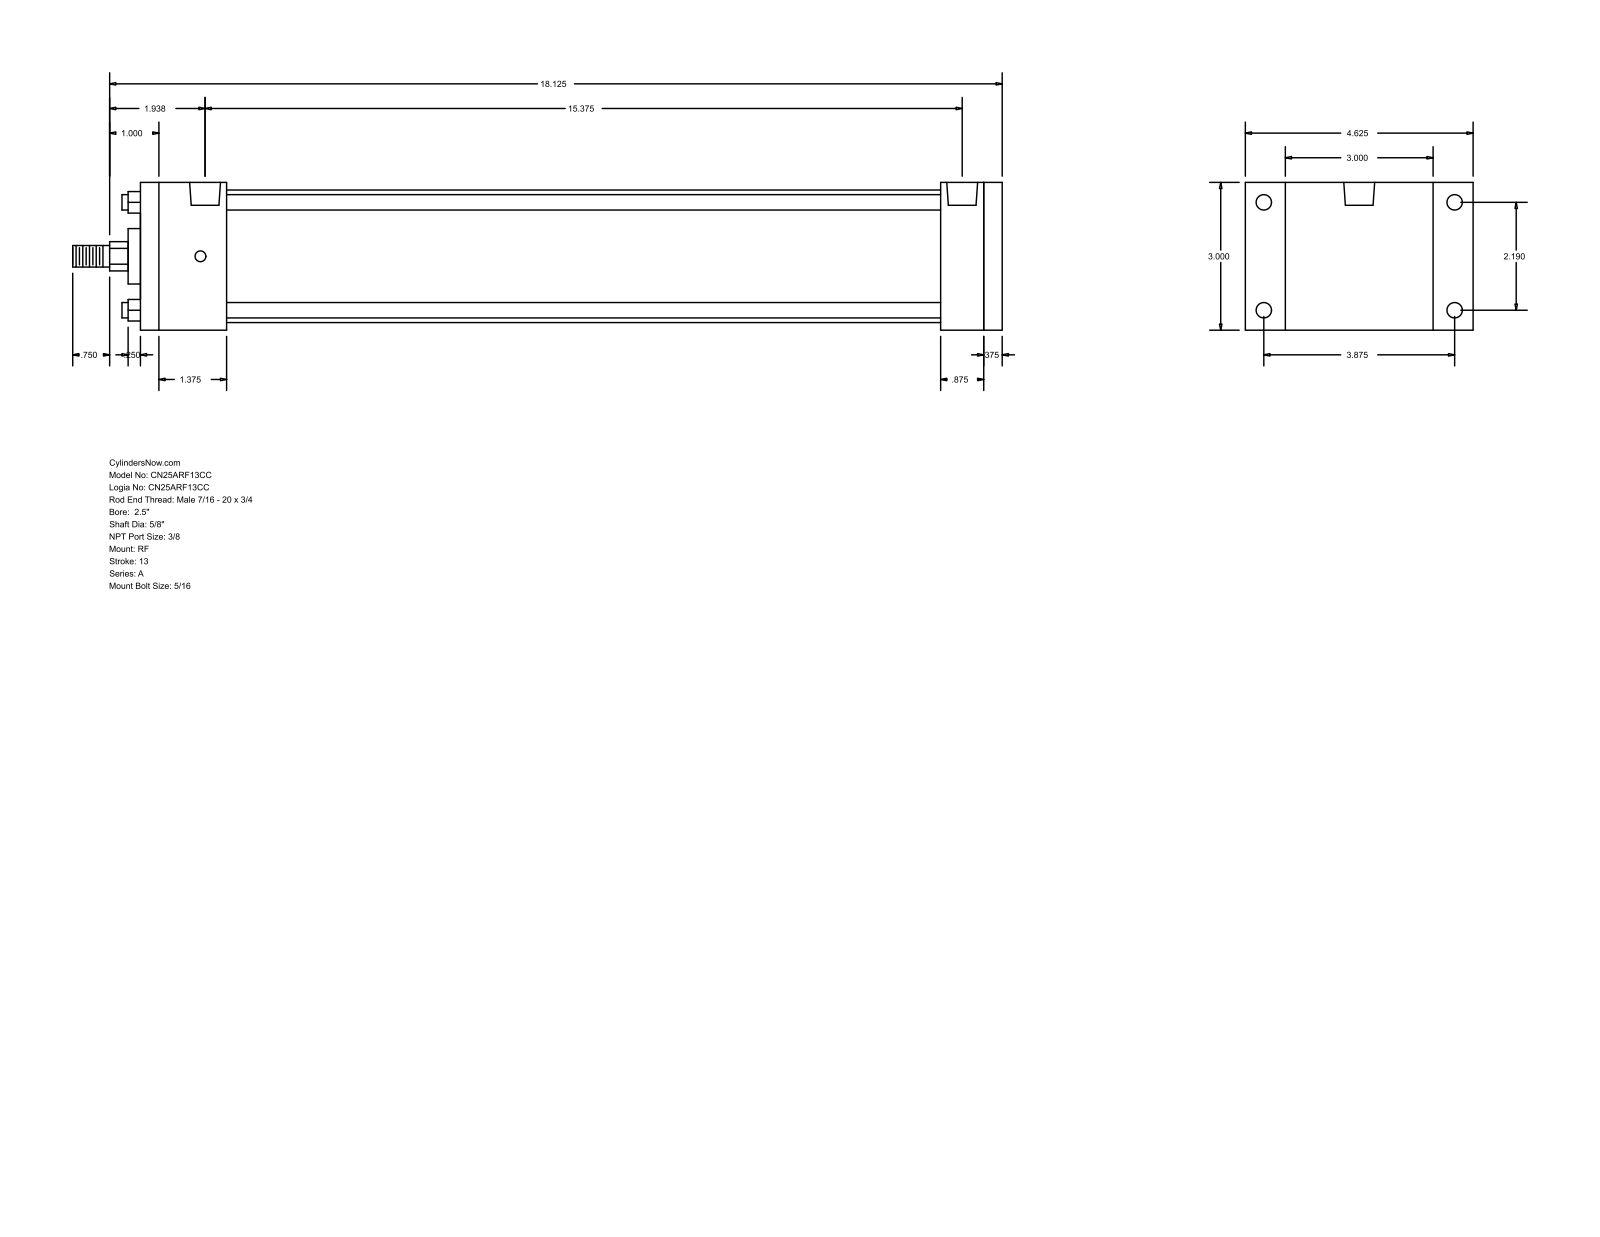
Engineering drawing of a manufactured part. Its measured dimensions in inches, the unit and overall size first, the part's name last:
Units: inches
Overall size (bounding box): 18.875 × 4.625 × 3
Round holes (diameter × count): ⌀0.219 ×4, ⌀0.313 ×4, ⌀0.627 ×2
Round bosses / shafts (diameter × count): ⌀0.313 ×4, ⌀2.69 ×1, ⌀1.125 ×1, ⌀0.625 ×1, ⌀0.437 ×1
Partial cylindrical surfaces — rounded edges, fillets, slot ends (radius × count): R0.297 ×1
Main face-to-face distances: 3, 17.5, 0.375, 17.125, 1.75, 16.25, 14.5, 15.375, 15.75, 0.875
Hole centre spacings: 0.094, 2.19, 3.875, 4.451, 15.469, 15.563, 15.375
Bodies: 0 solids, 92 faces (64 planar, 28 cylindrical, 0 other)
Part name (STEP PRODUCT): A_RF__0250_0.625
STEP written by: GSSL Pune (CONFIG_CONTROL_DESIGN)
